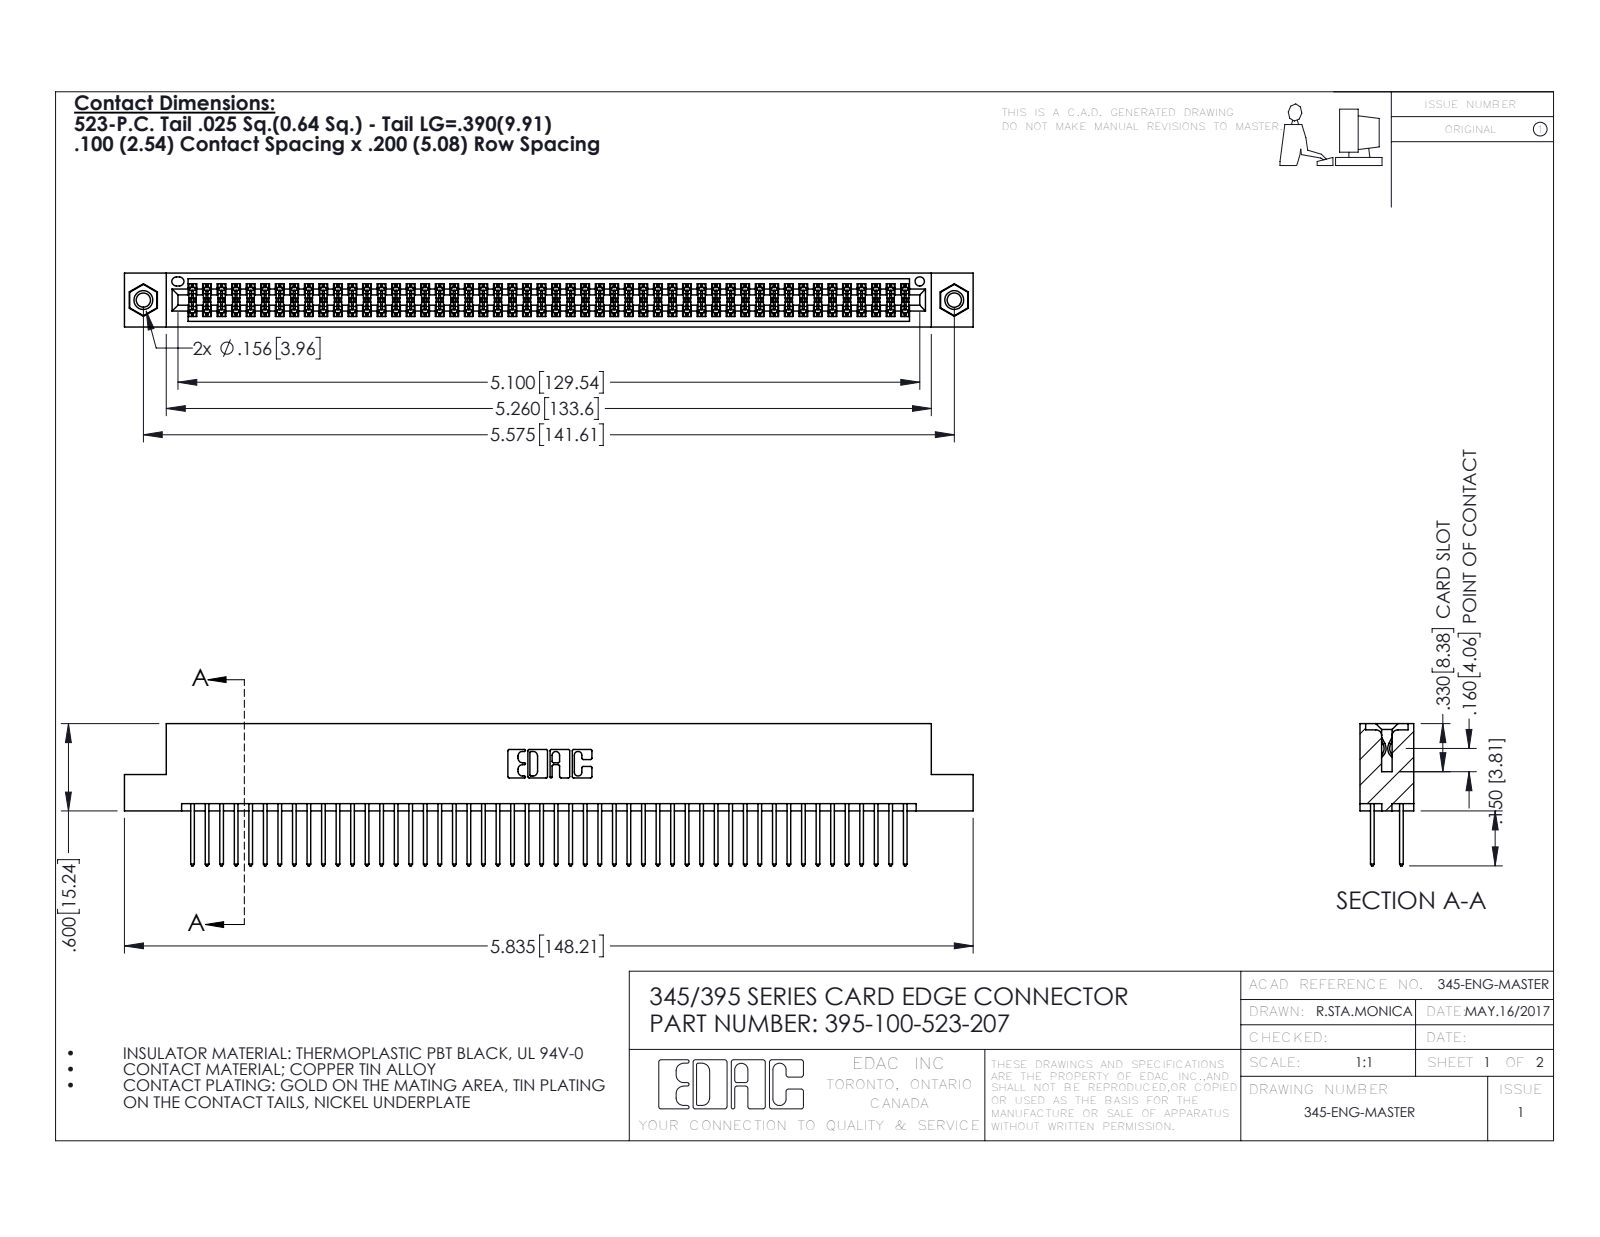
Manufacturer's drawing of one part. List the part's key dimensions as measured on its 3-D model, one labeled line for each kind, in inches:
Part name (STEP PRODUCT): 345-250-001_345-250-005-103; 345-292-001_345-293-123; 395-100-523-207; 345 Part_Flush Mounting Lugs - 0.156 Dia-TI
STEP written by: SolidWorks 2016 (CONFIG_CONTROL_DESIGN)
Units: inches
Bodies: 103 solids, 5186 faces (3412 planar, 1758 cylindrical, 16 other)
Overall size (bounding box): 5.835 × 0.977 × 0.37
Volume: 0.895 in³ · Surface area: 35.3 in²
Round holes (diameter × count): ⌀0.098 ×2, ⌀0.125 ×2, ⌀0.156 ×2, ⌀0.064 ×1
Round bosses / shafts (diameter × count): ⌀0.155 ×2
Partial cylindrical surfaces — rounded edges, fillets, slot ends (radius × count): R0.006 ×150, R0.01 ×100, R0.01 ×22, R0.007 ×6, R0.031 ×6, R0.026 ×3, R0.014 ×2, R0.019 ×2
Main face-to-face distances: 0.072, 0.298, 0.2, 0.098, 0.272, 0.025, 0.37, 0.225, 0.175, 0.149
Hole centre spacings: 0.27, 5.339, 5.575
